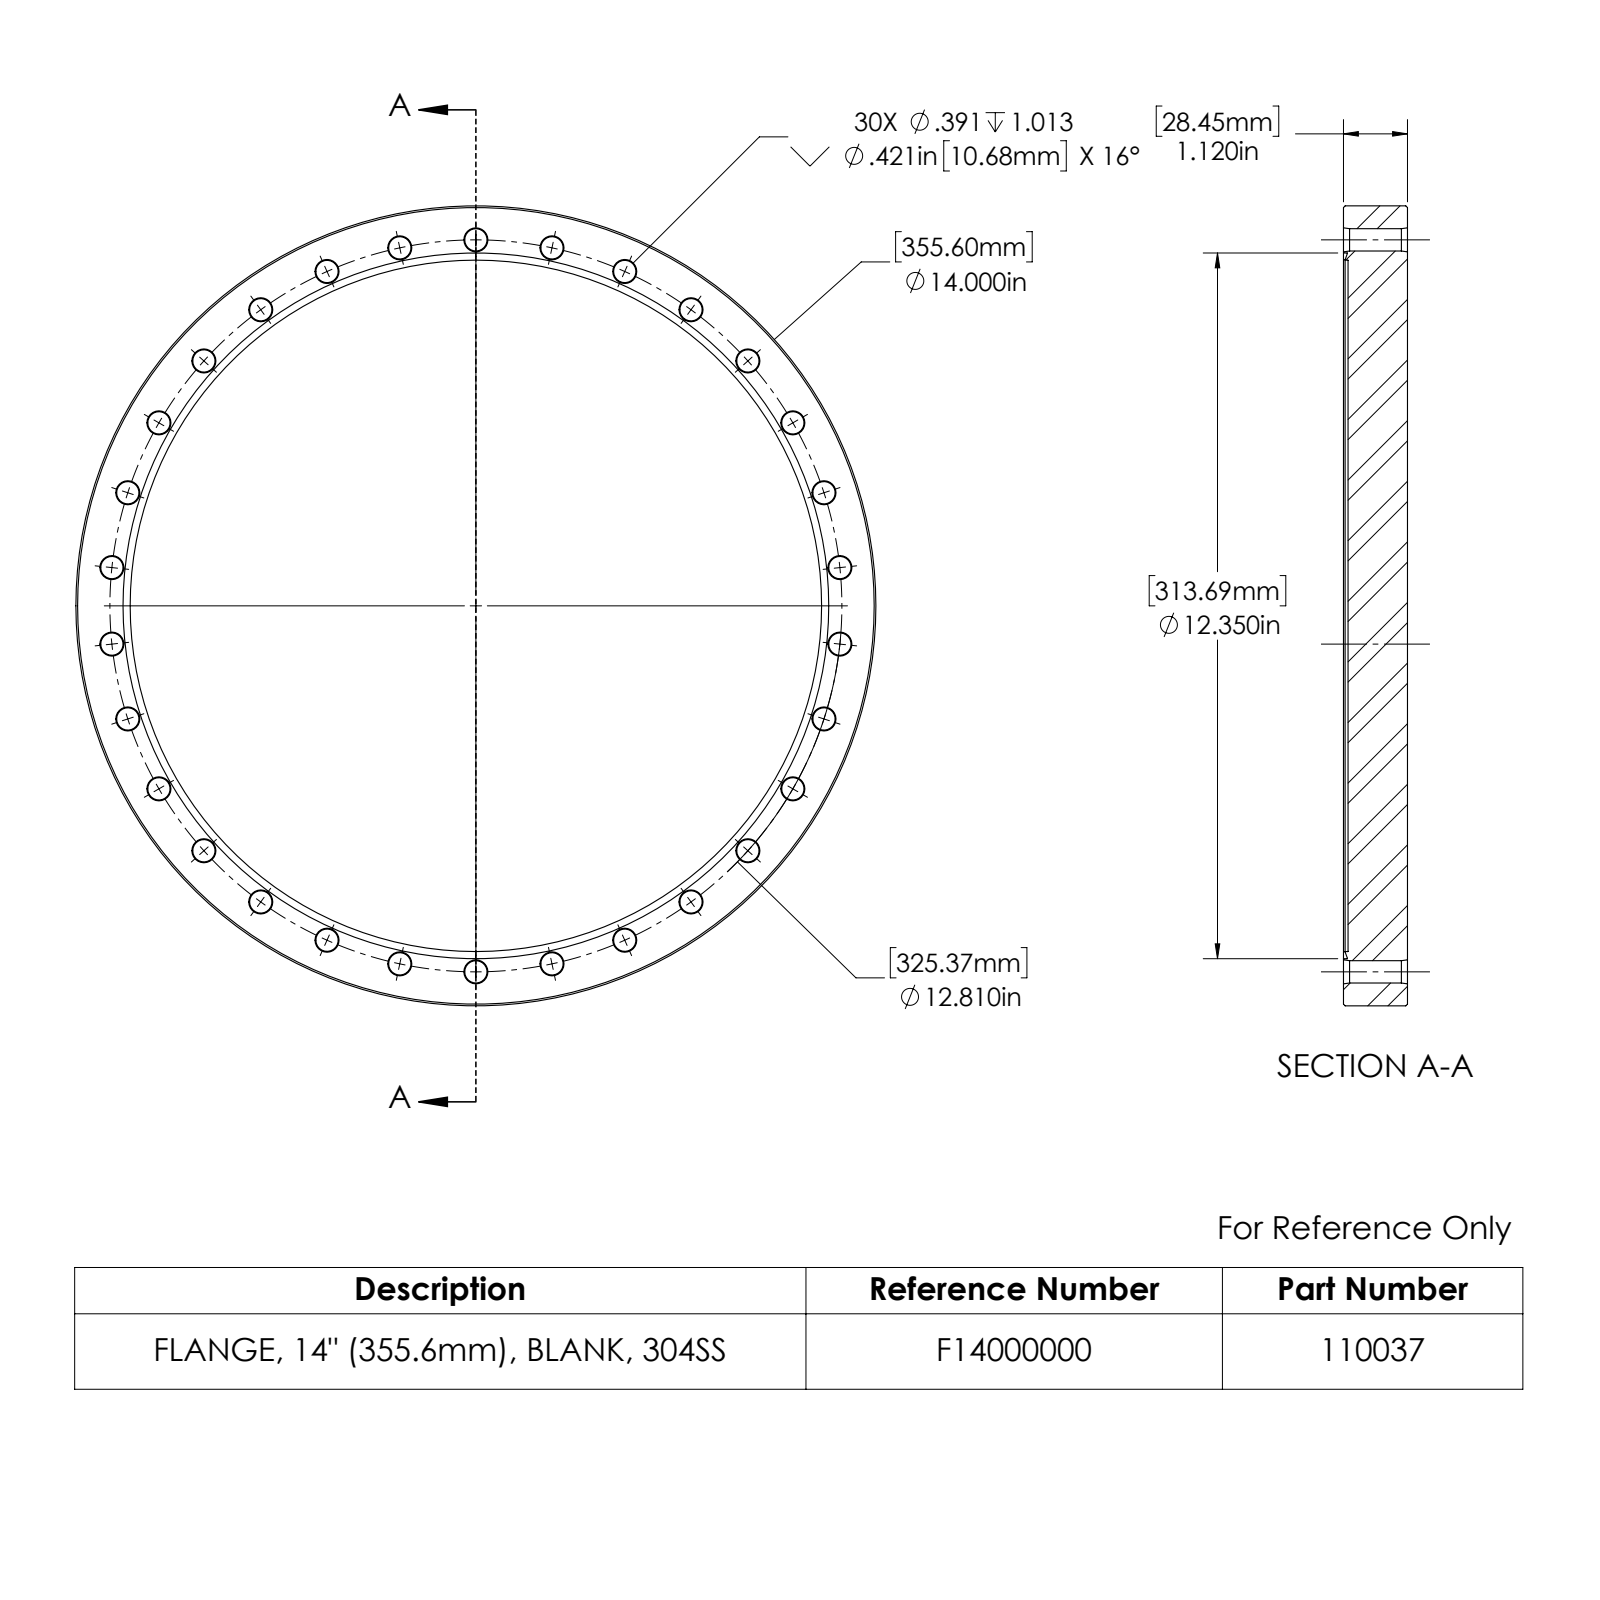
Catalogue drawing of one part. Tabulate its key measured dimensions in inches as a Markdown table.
| quantity | value |
| --- | --- |
| part name | 110037 |
| STEP written by | SolidWorks 2022 (AUTOMOTIVE_DESIGN) |
| units | inches |
| bodies | 1 solid, 201 faces (3 planar, 66 cylindrical, 132 other) |
| overall size | 14 × 14 × 1.12 |
| volume | 158.9 in³ |
| surface area | 393.6 in² |
| round holes (diameter × count) | 0.391 × 30, 12.1 × 1, 12.35 × 1 |
| round bosses / shafts (diameter × count) | 14 × 1 |
| main face-to-face distances | 1.04, 0.08, 1.12 |
| hole center spacings | 1.339, 7.53, 10.363, 2.663, 3.959, 12.74, 5.21, 8.572 |
